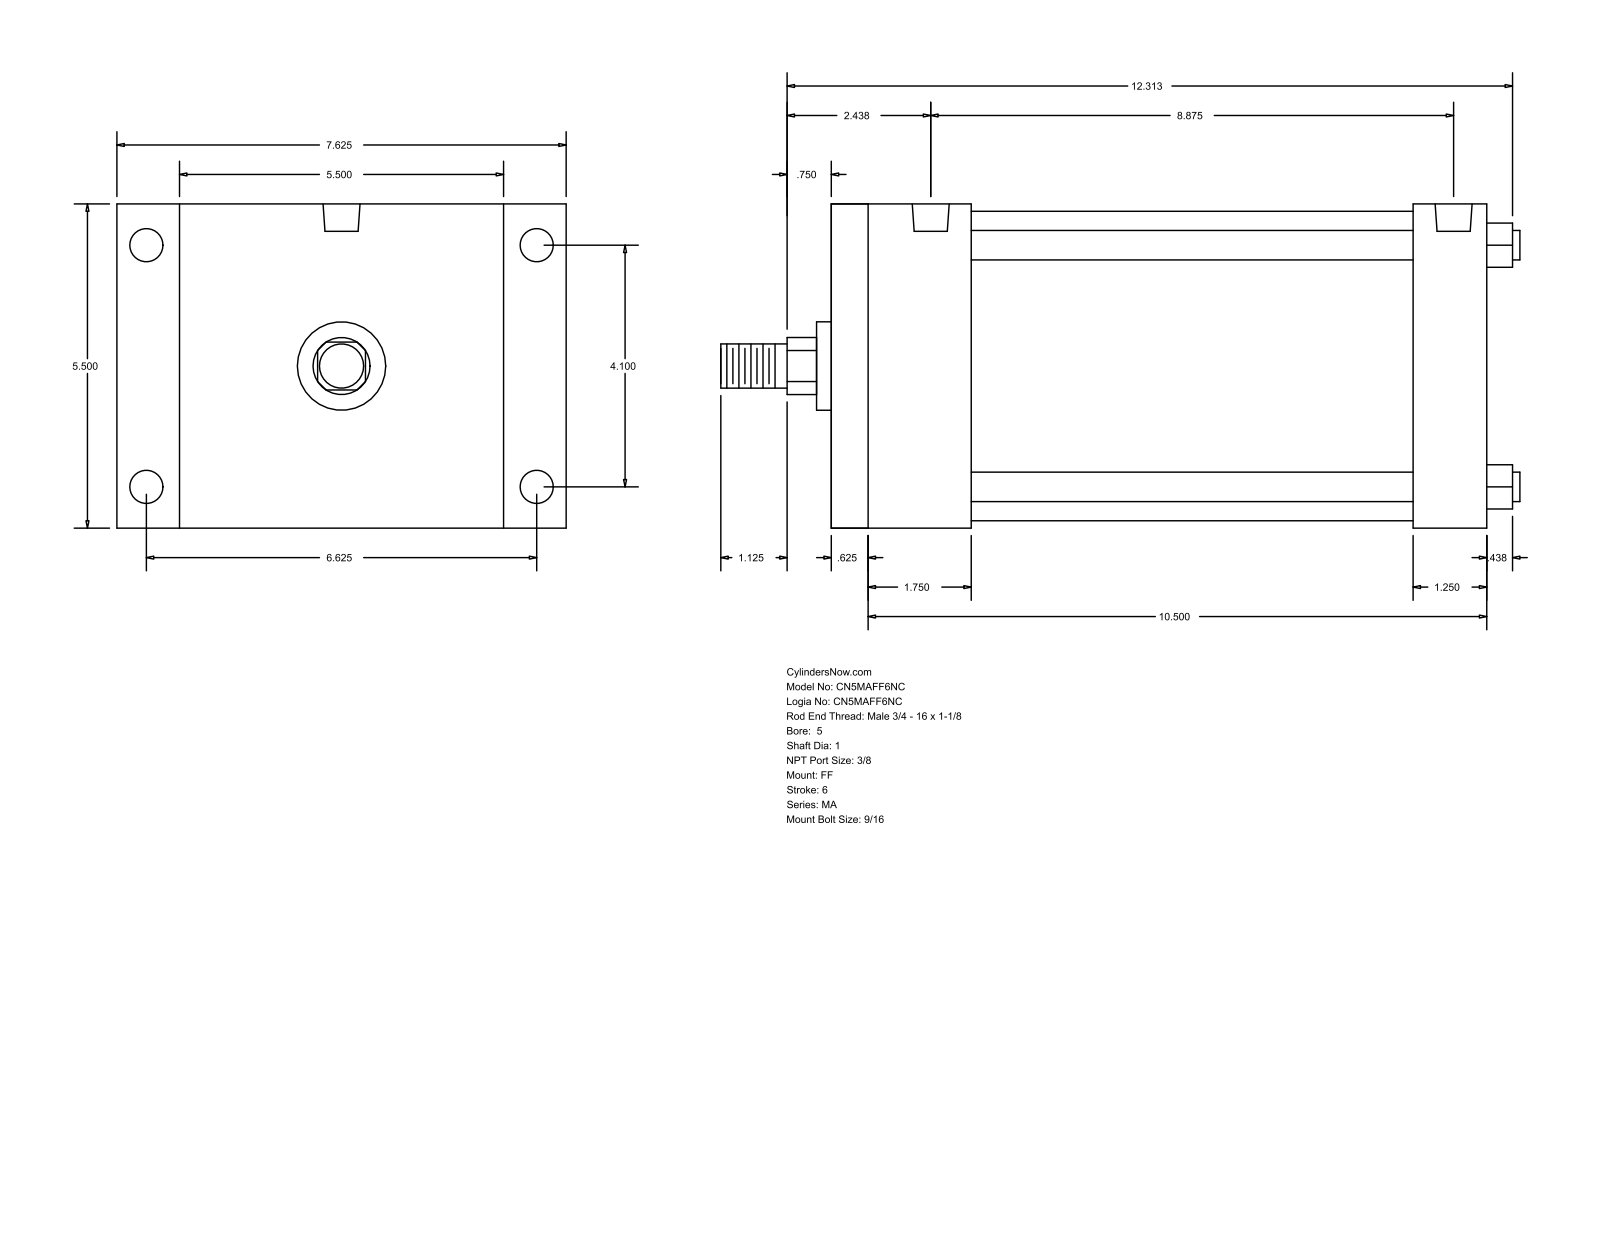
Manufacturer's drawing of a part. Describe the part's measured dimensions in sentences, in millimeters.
The part is named "MA_FF__0500_1". Its 3-D file was written by "GSSL Pune (CONFIG_CONTROL_DESIGN)". It is 0 solids with 92 faces: 64 planar, 28 cylindrical and 0 other. Overall it measures 344.49 by 193.68 by 139.7 millimeters. Round holes: 4 of diameter 11.11, 4 of diameter 14.29, 2 of diameter 15.93. Round bosses or shafts: 4 of diameter 12.7, 1 of diameter 133.35, 1 of diameter 38.1, 1 of diameter 25.4, 1 of diameter 19.05. Partial cylindrical surfaces (rounded edges, fillets, slot ends): 1 of radius 12.29. The main face-to-face distances are 139.7, 282.57, 15.87, 266.7, 250.83, 234.96, 31.74, 60.33, 44.46, 190.5. The hole center spacings are 104.14, 168.28, 197.9, 215.9, 4.76, 4.77, 220.66, 220.67.
